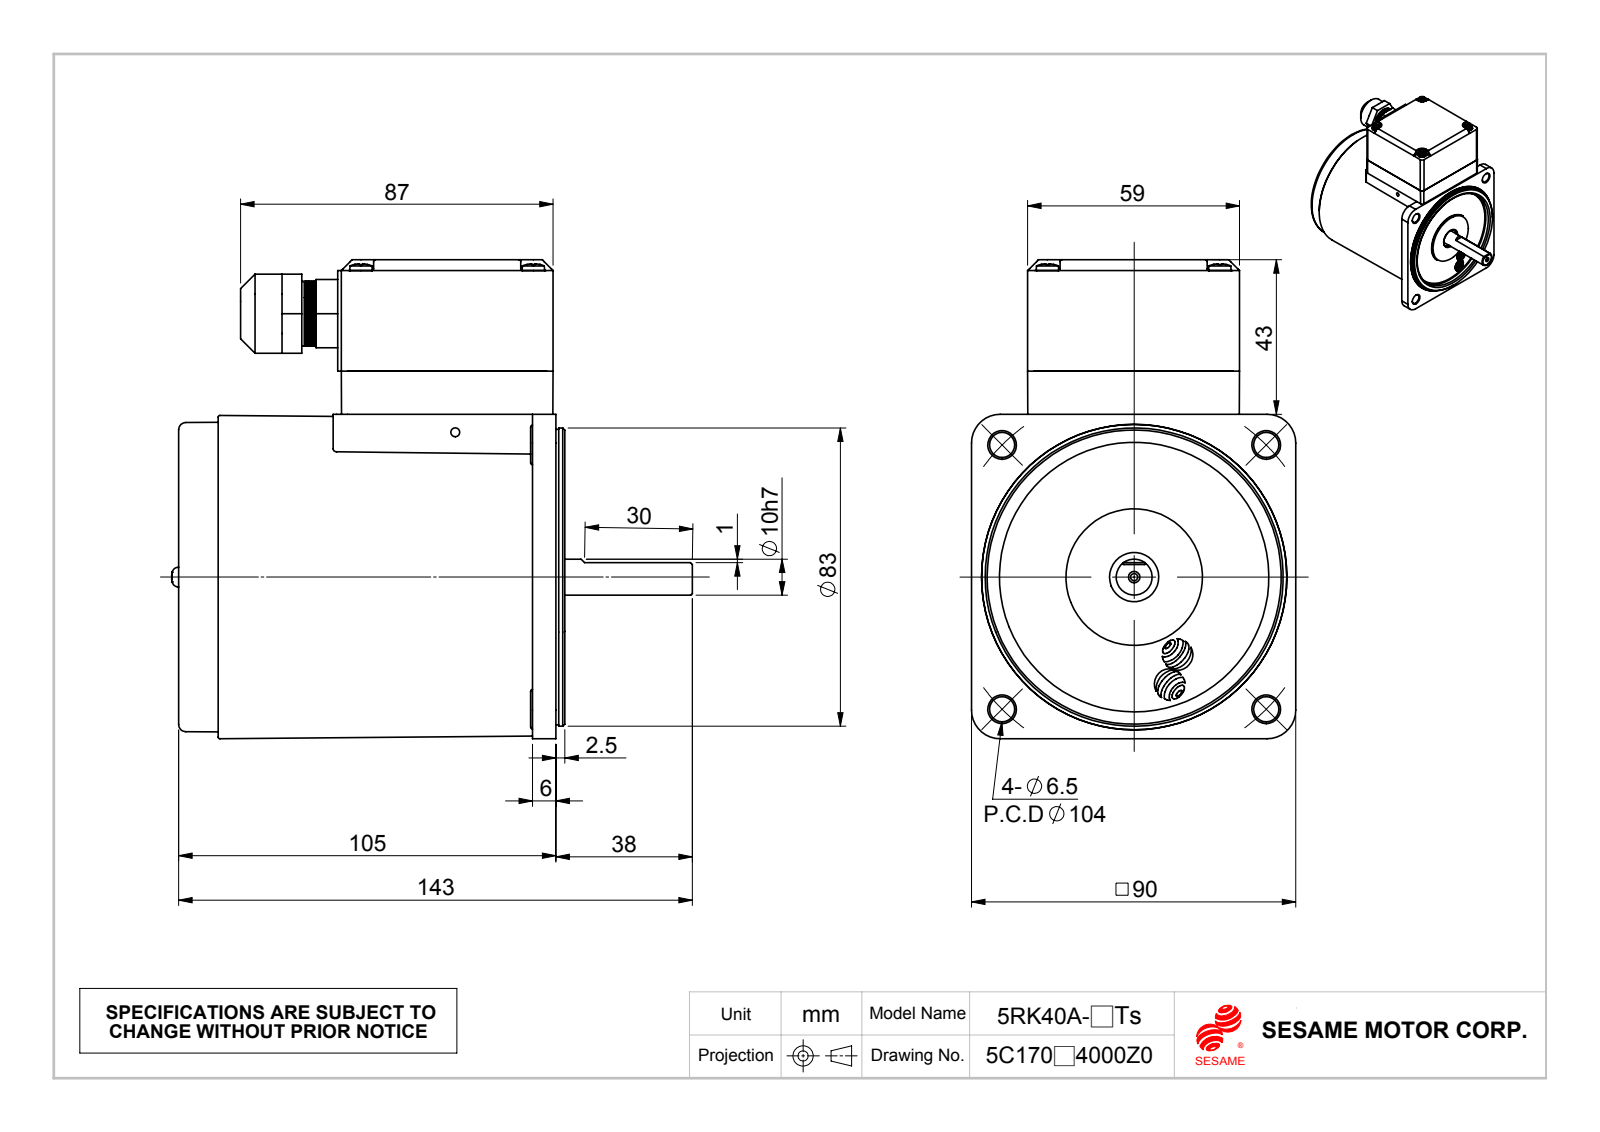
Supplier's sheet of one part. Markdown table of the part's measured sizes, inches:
| quantity | value |
| --- | --- |
| part name | 成品180度; 펥짰웰찿M5즤45x1t_Default; 40A; M540Ts-RK (+1 more) |
| STEP written by | SolidWorks 2010 (CONFIG_CONTROL_DESIGN) |
| units | inches |
| bodies | 14 solids, 2622 faces (242 planar, 969 cylindrical, 1411 other) |
| overall size | 5.707 × 5.248 × 3.555 |
| volume | 18.87 in³ |
| surface area | 200.7 in² |
| round holes (diameter × count) | 0.13 × 4, 0.138 × 4, 0.154 × 4, 0.169 × 4, 0.244 × 4, 0.276 × 4, 0.098 × 3, 0.157 × 2, 0.079 × 1, 0.433 × 1, 0.472 × 1, 0.539 × 1 |
| round bosses / shafts (diameter × count) | 0.118 × 6, 0.248 × 4, 0.217 × 2, 3.316 × 1, 3.268 × 1, 3.236 × 1, 1.772 × 1, 1.496 × 1 |
| partial cylindrical surfaces (radius × count) | 0.079 × 12, 0.012 × 8, 0.02 × 8, 0.031 × 8, 0.059 × 8, 0.065 × 8, 0.115 × 8, 0.157 × 6 |
| main face-to-face distances | 0.039, 4.035, 0.472, 3.858, 3.996, 0.177, 0.138, 4.075, 0.059, 0.098 |
| hole center spacings | 2.16, 0.527, 0.689, 0.974, 1.273, 1.359, 1.634, 1.89 |
